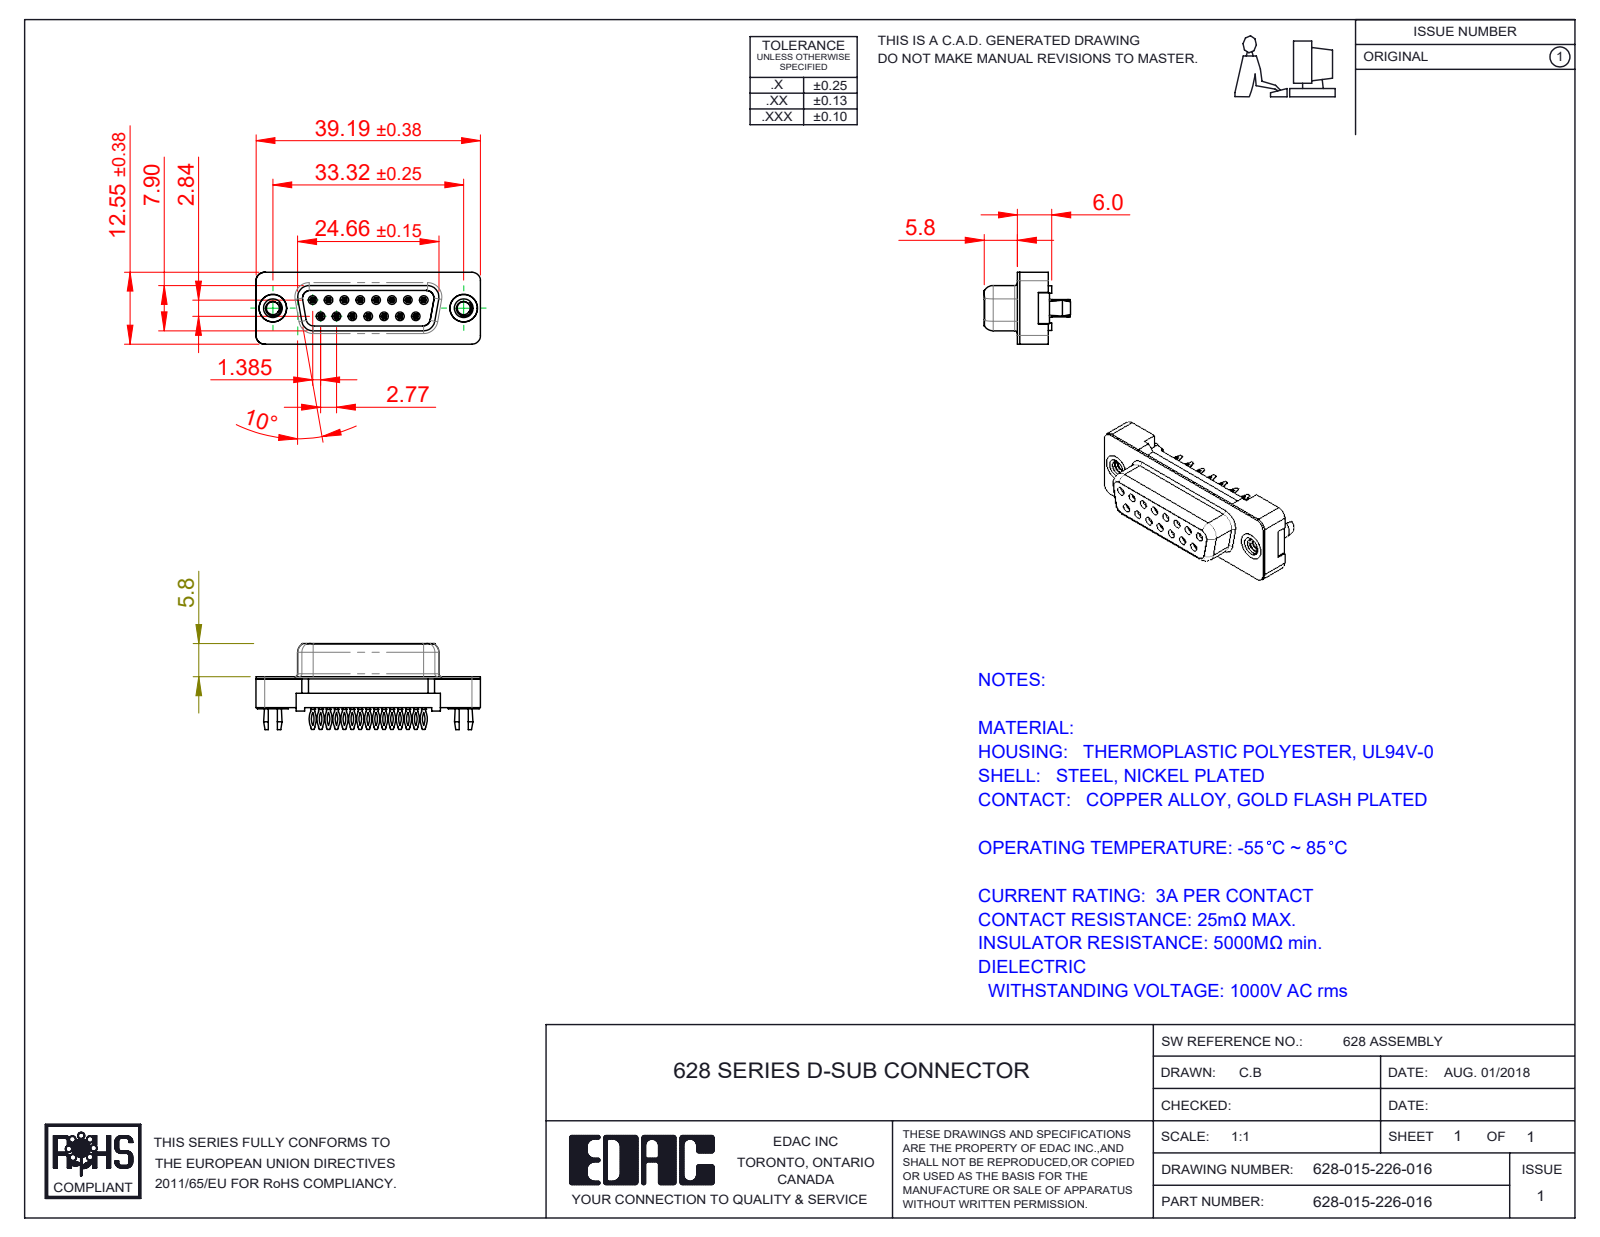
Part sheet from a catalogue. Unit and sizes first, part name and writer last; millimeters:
Units: millimetres
Overall size (bounding box): 39.2 × 15.05 × 12.55
Round holes (diameter × count): ⌀0.9 ×15, ⌀2.26 ×2, ⌀3.05 ×2, ⌀4 ×2, ⌀4.8 ×2, ⌀5 ×2
Round bosses / shafts (diameter × count): ⌀4.9 ×2
Partial cylindrical surfaces — rounded edges, fillets, slot ends (radius × count): R0.25 ×60, R2.92 ×30, R3.33 ×30, R0.5 ×19, R0.3 ×15, R1.35 ×12, R1.5 ×8, R0.9 ×4
Main face-to-face distances: 0.4, 5.54, 2, 2.5, 6.2, 2.77, 0.68, 5.52, 2.68, 3.52
Hole centre spacings: 3.16, 2.77, 5.54, 8.31, 11.08, 5.03, 5.04, 7.48
Volume: 2 482 mm³ · Surface area: 5 979 mm²
Bodies: 19 solids, 1611 faces (664 planar, 398 cylindrical, 549 other)
Part name (STEP PRODUCT): 628 Plastic Body Housing_15 Contacts; 628 PB 4-40 Threaded Rivet with Boardlock; 628-015-226-016; 628 PB Shell_15 Contacts (+2 more)
STEP written by: SolidWorks 2020 (CONFIG_CONTROL_DESIGN)
